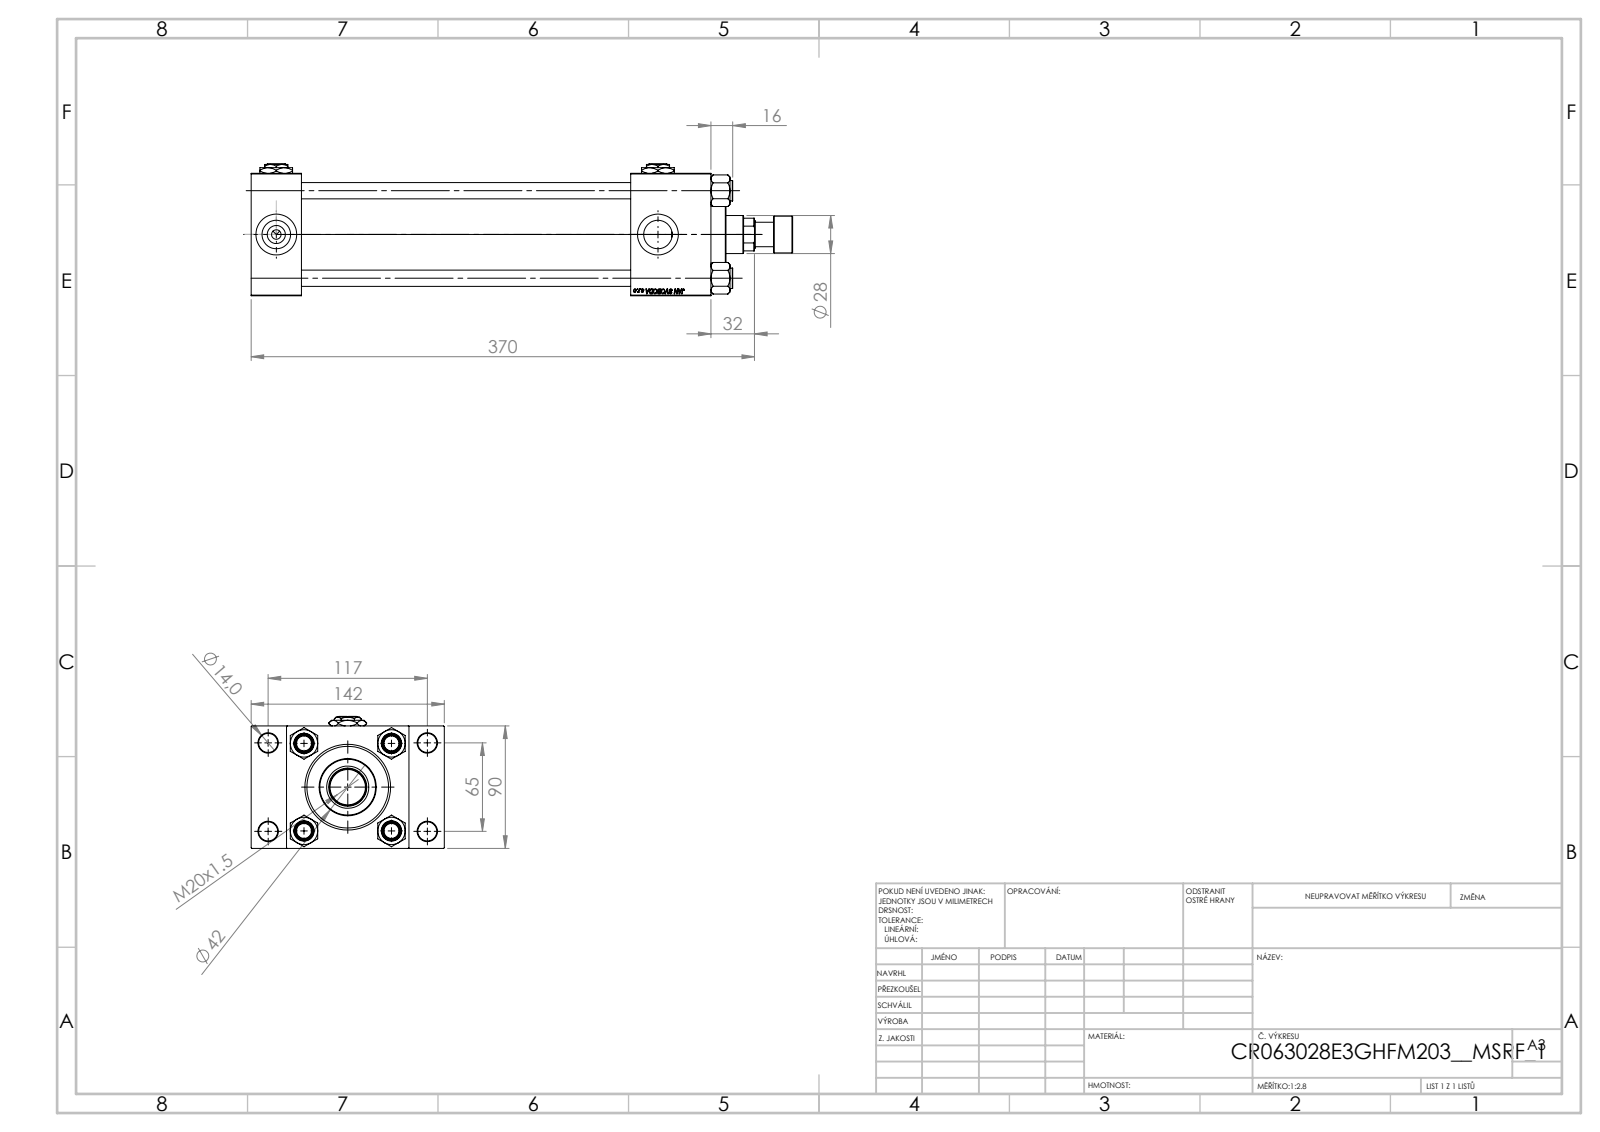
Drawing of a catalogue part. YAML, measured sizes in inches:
part_name: "NUT_M5_E; Zatka_pro_OIL_PORT; V215CR_E_Body; V215CR_VCP_E (+3 more)"
step_written_by: "SolidWorks 2019 (CONFIG_CONTROL_DESIGN)"
units: inches
bodies: {solids: 14, faces: 1251, planar: 550, cylindrical: 101, other: 600}
overall_size: [15.669, 5.591, 3.819]
volume: 86.59
surface_area: 518.1
round_holes:
  - {diameter: 0.472, count: 4}
  - {diameter: 0.551, count: 4}
  - {diameter: 0.825, count: 4}
  - {diameter: 1.181, count: 4}
  - {diameter: 0.276, count: 3}
  - {diameter: 0.728, count: 1}
  - {diameter: 1.102, count: 1}
  - {diameter: 1.22, count: 1}
  - {diameter: 1.969, count: 1}
  - {diameter: 2.362, count: 1}
  - {diameter: 2.48, count: 1}
round_bosses_or_shafts:
  - {diameter: 0.591, count: 4}
  - {diameter: 2.717, count: 1}
  - {diameter: 1.654, count: 1}
  - {diameter: 1.063, count: 1}
  - {diameter: 0.709, count: 1}
face_to_face_distances: [3.543, 1.457, 13.307, 11.85, 1.024, 4.567, 2.323, 10.984, 9.528, 12.177]
hole_center_spacings: [1.037, 1.79, 2.531, 2.635, 2.748, 3.569, 4.383, 2.559]
